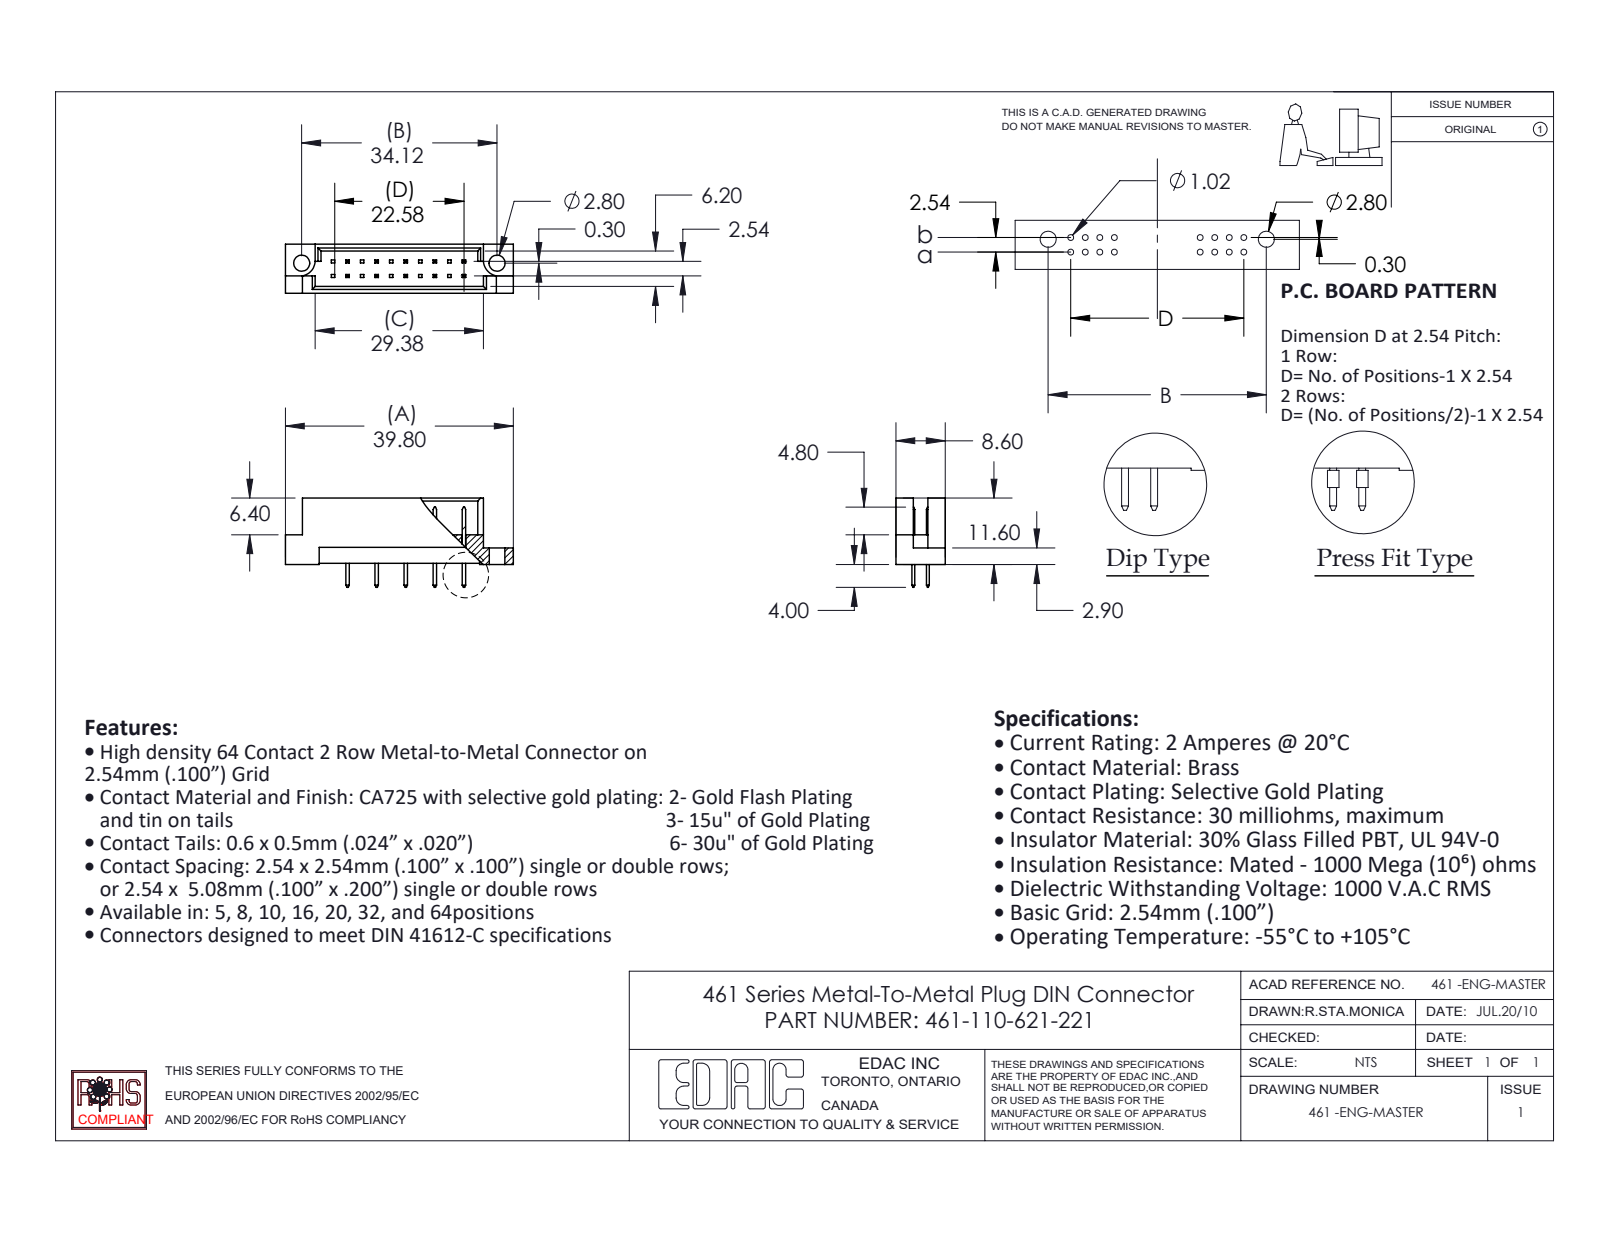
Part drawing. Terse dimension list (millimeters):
name: 461-290_21; 461-110-621-221; 461 Part_20
written by: SolidWorks 2020 (CONFIG_CONTROL_DESIGN)
unit: mm
bodies: 11 solids, 268 faces (262 planar, 6 cylindrical, 0 other)
size: 39.8 × 15.6 × 8.6
volume: 1 946 mm³; area: 2 642 mm²
holes: 2× ⌀2.8
rounds: 2× R2.8
face distances: 1.2, 7.4, 8.6, 6.2, 5, 2.54, 5.08, 3.28, 5.32, 2.08
hole spacings: 34.12
